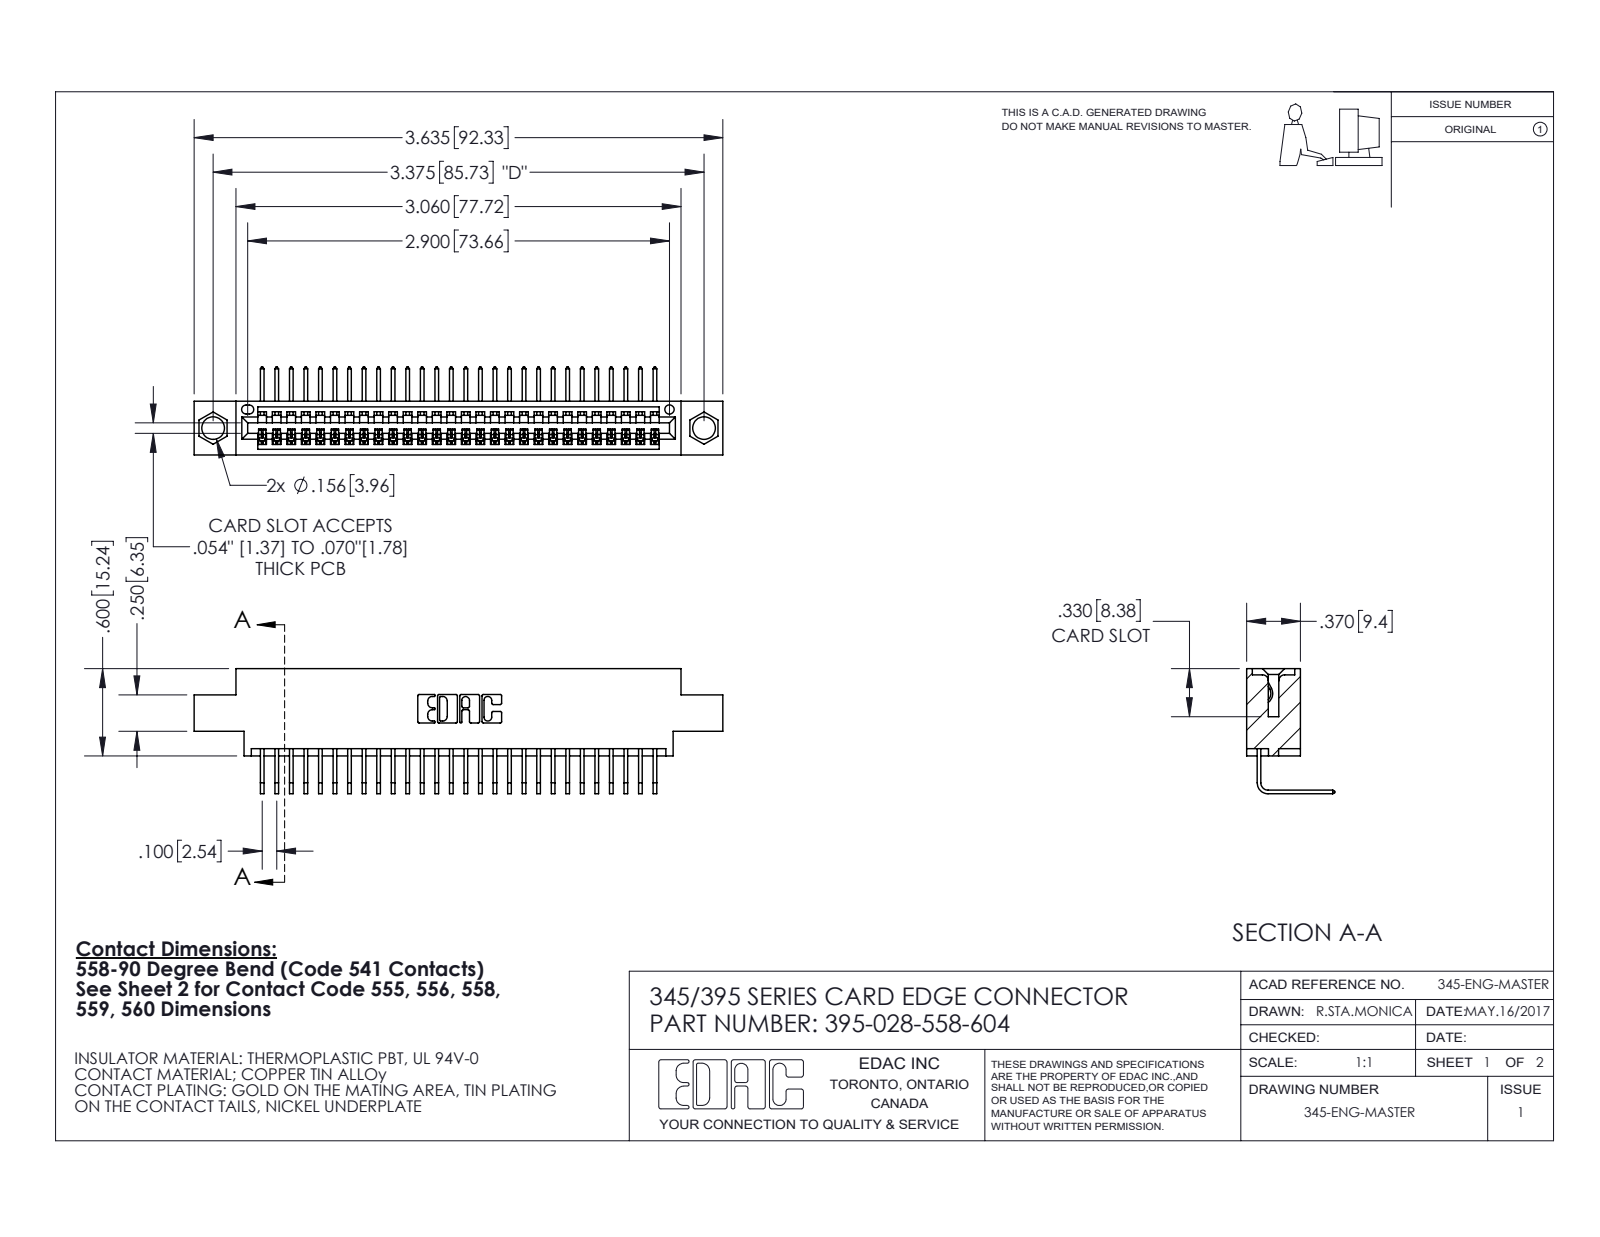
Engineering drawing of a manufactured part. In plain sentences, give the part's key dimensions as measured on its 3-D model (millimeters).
The part is named "345-292-001_558 Tail - 2; 395-028-558-604; 345 Part_0.170 Offset - 0.156 Dia-TI". Its 3-D file was written by "SolidWorks 2020 (CONFIG_CONTROL_DESIGN)". It is 29 solids with 1824 faces: 1274 planar, 550 cylindrical and 0 other. Overall it measures 92.3 by 21.8 by 15.4 millimeters. Its volume is 8 520 cubic millimeters and its surface area 11 660 square millimeters. Round holes: 2 of diameter 4, 1 of diameter 1.6. Partial cylindrical surfaces (rounded edges, fillets, slot ends): 56 of radius 0.2, 22 of radius 0.3, 6 of radius 0.2, 6 of radius 0.8, 3 of radius 0.7, 2 of radius 0.8, 2 of radius 1, 1 of radius 0.4. The main face-to-face distances are 1.8, 7.6, 9.4, 5.1, 2.5, 6.9, 0.6, 5.7, 4.4, 3.8. The hole center spacings are 6.9, 79.8, 85.7.
